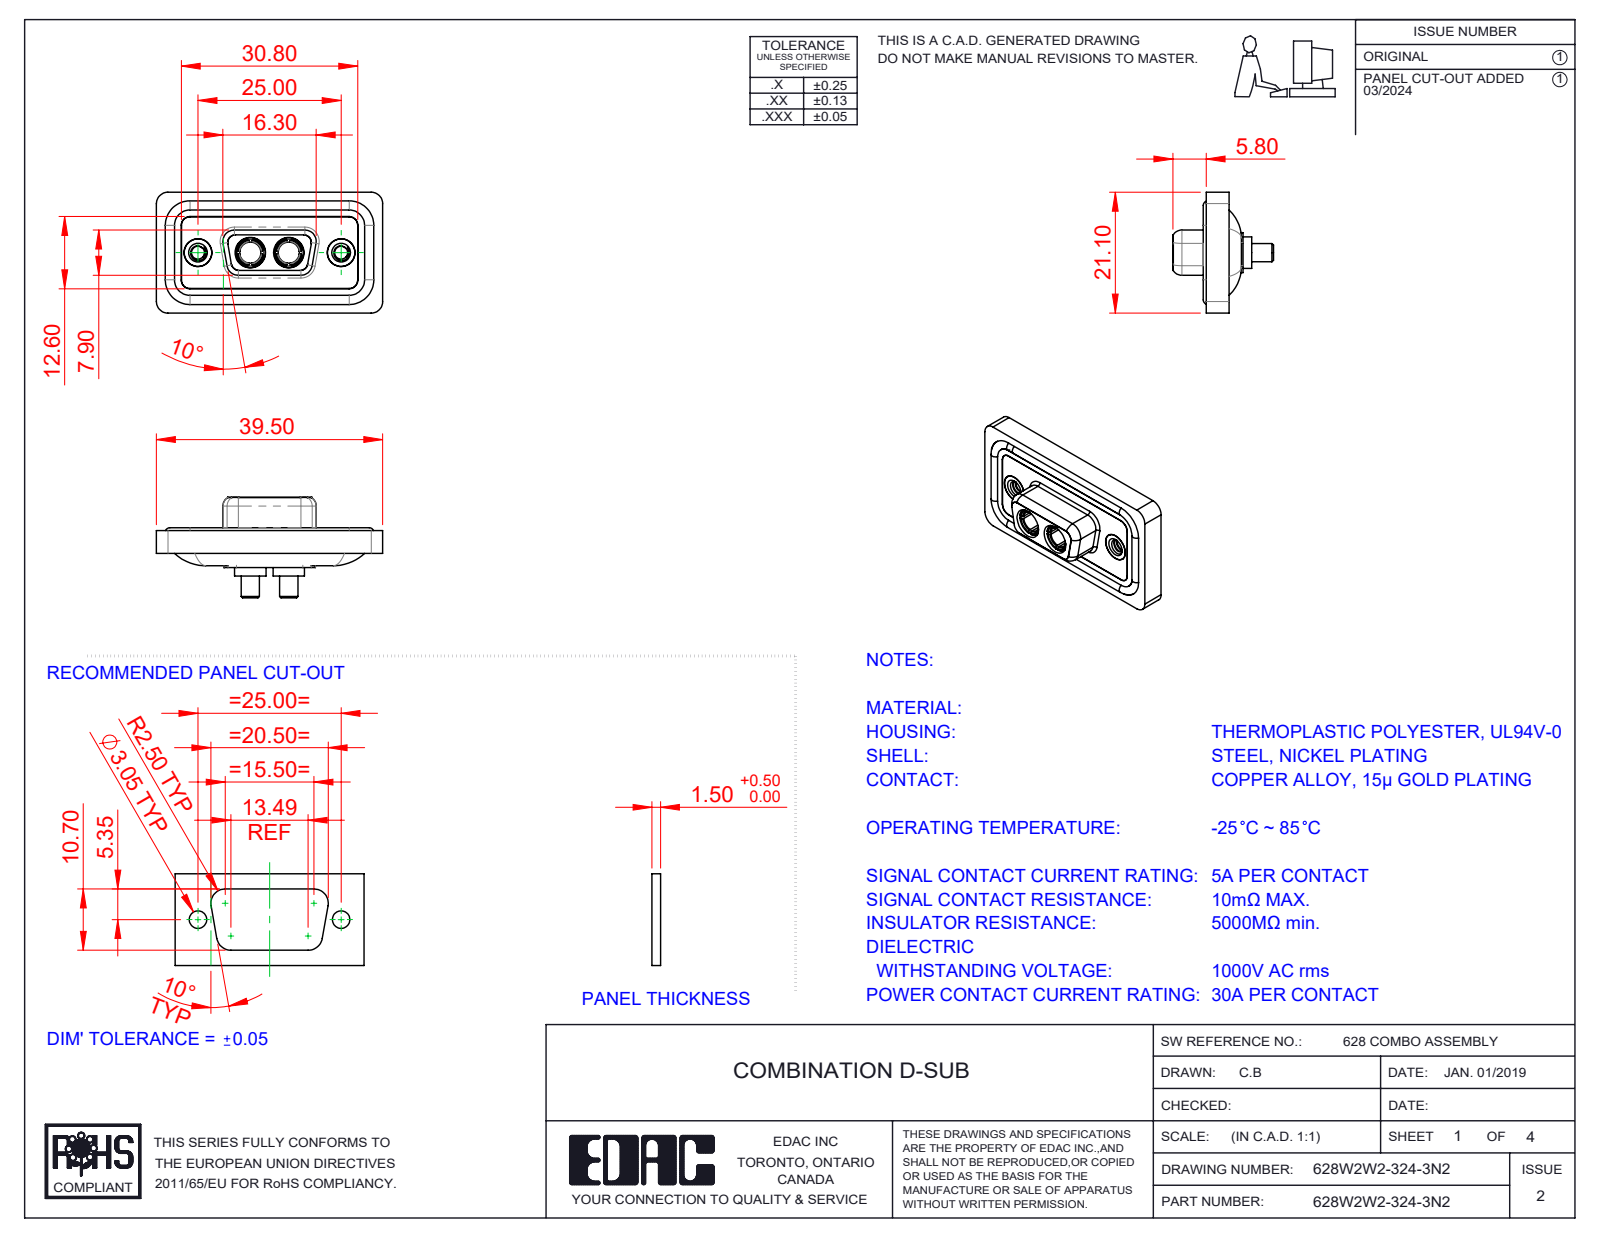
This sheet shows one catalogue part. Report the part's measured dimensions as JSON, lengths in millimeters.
{"part_name": "628Combo Waterproof Housing_09 Contacts; 628Combo Shell Rear_09 Contacts; 628Combo Housing_2W2; 628Combo Threaded Rivet_2 (+3 more)", "step_written_by": "SolidWorks 2023 (CONFIG_CONTROL_DESIGN)", "units": "millimeters", "bodies": {"solids": 11, "faces": 534, "planar": 163, "cylindrical": 234, "other": 137}, "overall_size": [39.5, 21.1, 17.55], "volume_mm3": 4727, "surface_area_mm2": 7645, "round_holes": [[4.85, 4], [2.26, 2], [3.7, 2], [4, 2], [4.05, 2], [5, 2], [5.3, 2]], "round_bosses_or_shafts": [[1.6, 4], [5.5, 2], [5.2, 2], [4.96, 2], [4.95, 2], [4.8, 2], [4.75, 2], [3.75, 2]], "partial_cylinders_radius": [[1.5, 22], [2, 18], [1.35, 8], [1.6, 8], [0.25, 4], [0.5, 4], [0.6, 4], [0.65, 4]], "face_to_face_distances": [0.4, 1.8, 1.1, 2.9, 0.5, 1.6, 5.65, 7.45, 1.5, 5.35], "hole_center_spacings": [9.14, 15.86, 6.72, 25]}
